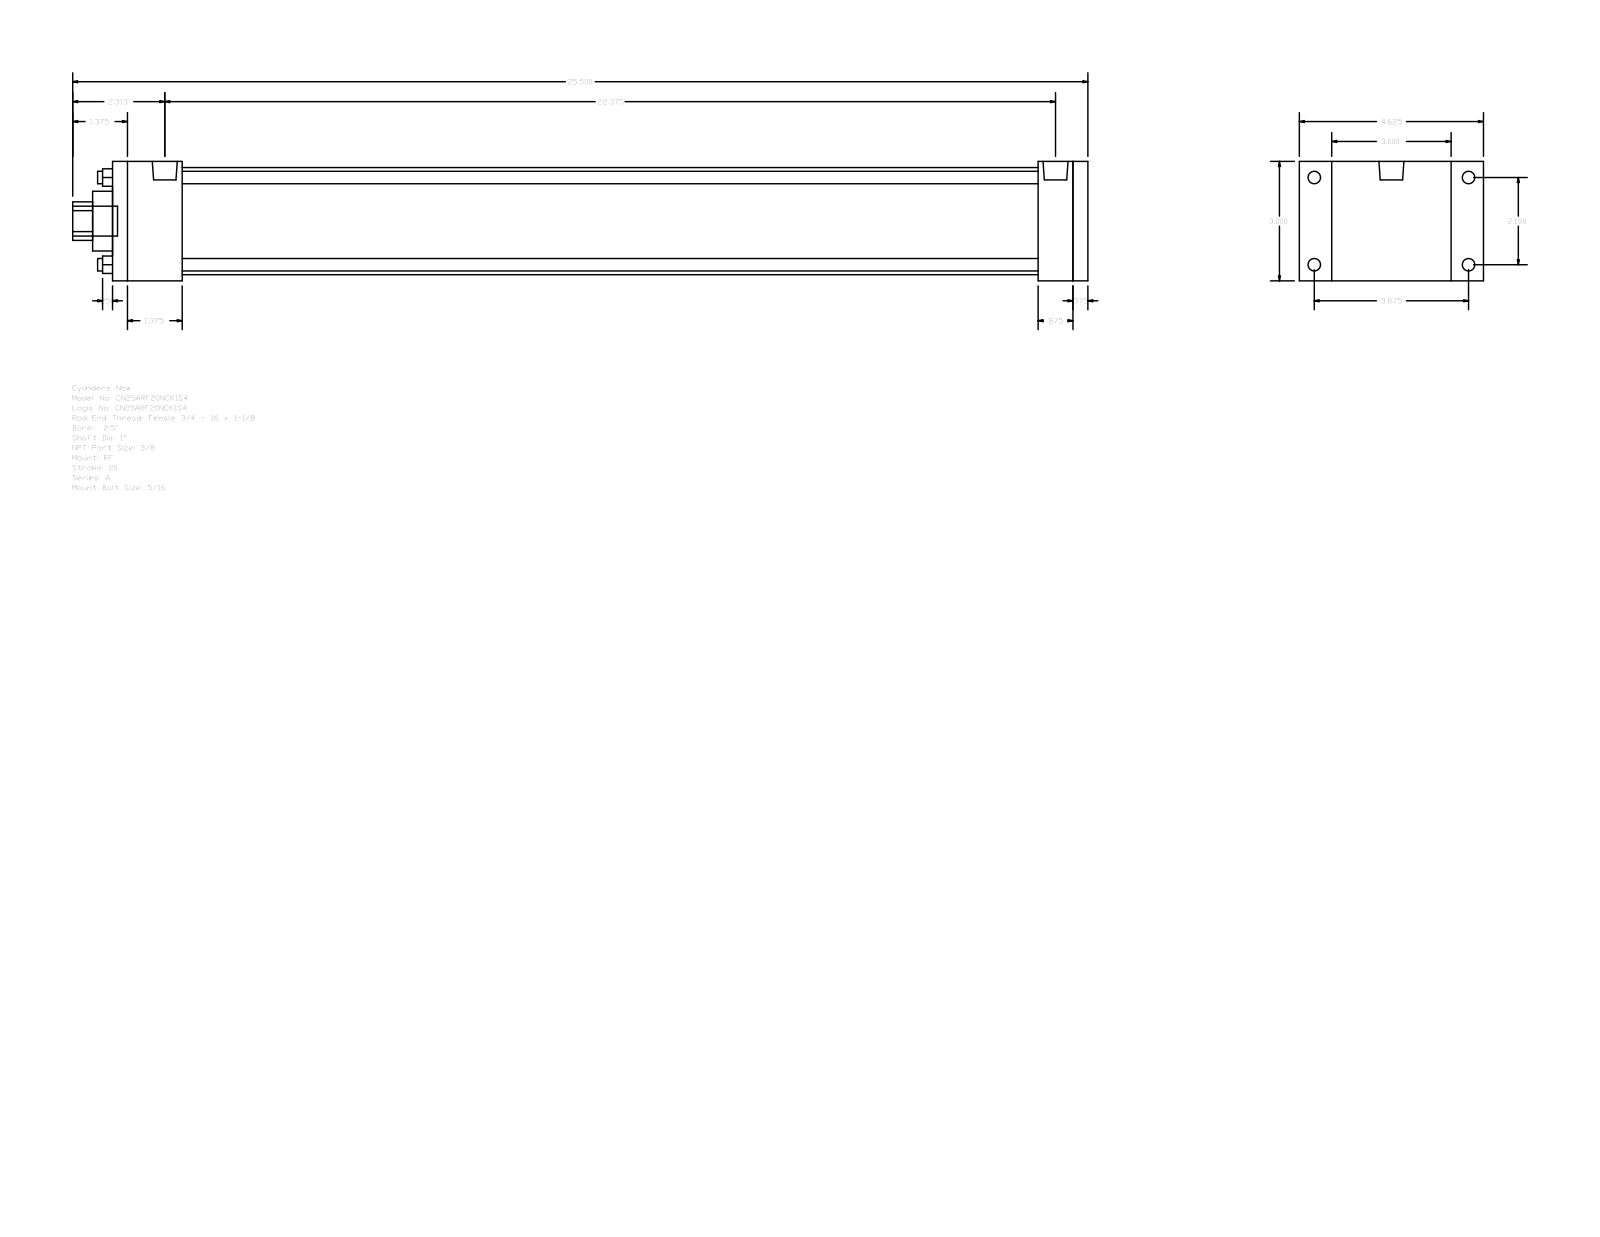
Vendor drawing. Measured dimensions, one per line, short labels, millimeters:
name: A_RF__0250_1
written by: GSSL Pune (CONFIG_CONTROL_DESIGN)
unit: mm
bodies: 0 solids, 92 faces (64 planar, 28 cylindrical, 0 other)
size: 647.7 × 117.47 × 76.2
holes: 4× ⌀7.94, 1× ⌀25.4, 1× ⌀38.1, 1× ⌀68.33
bosses: 4× ⌀7.94, 4× ⌀5.56, 2× ⌀15.93, 1× ⌀19.05
rounds: 1× R12.29
face distances: 76.2, 622.3, 9.53, 612.77, 44.45, 590.55, 546.1, 568.32, 577.85, 22.22
hole spacings: 39.33, 55.62, 78.66
